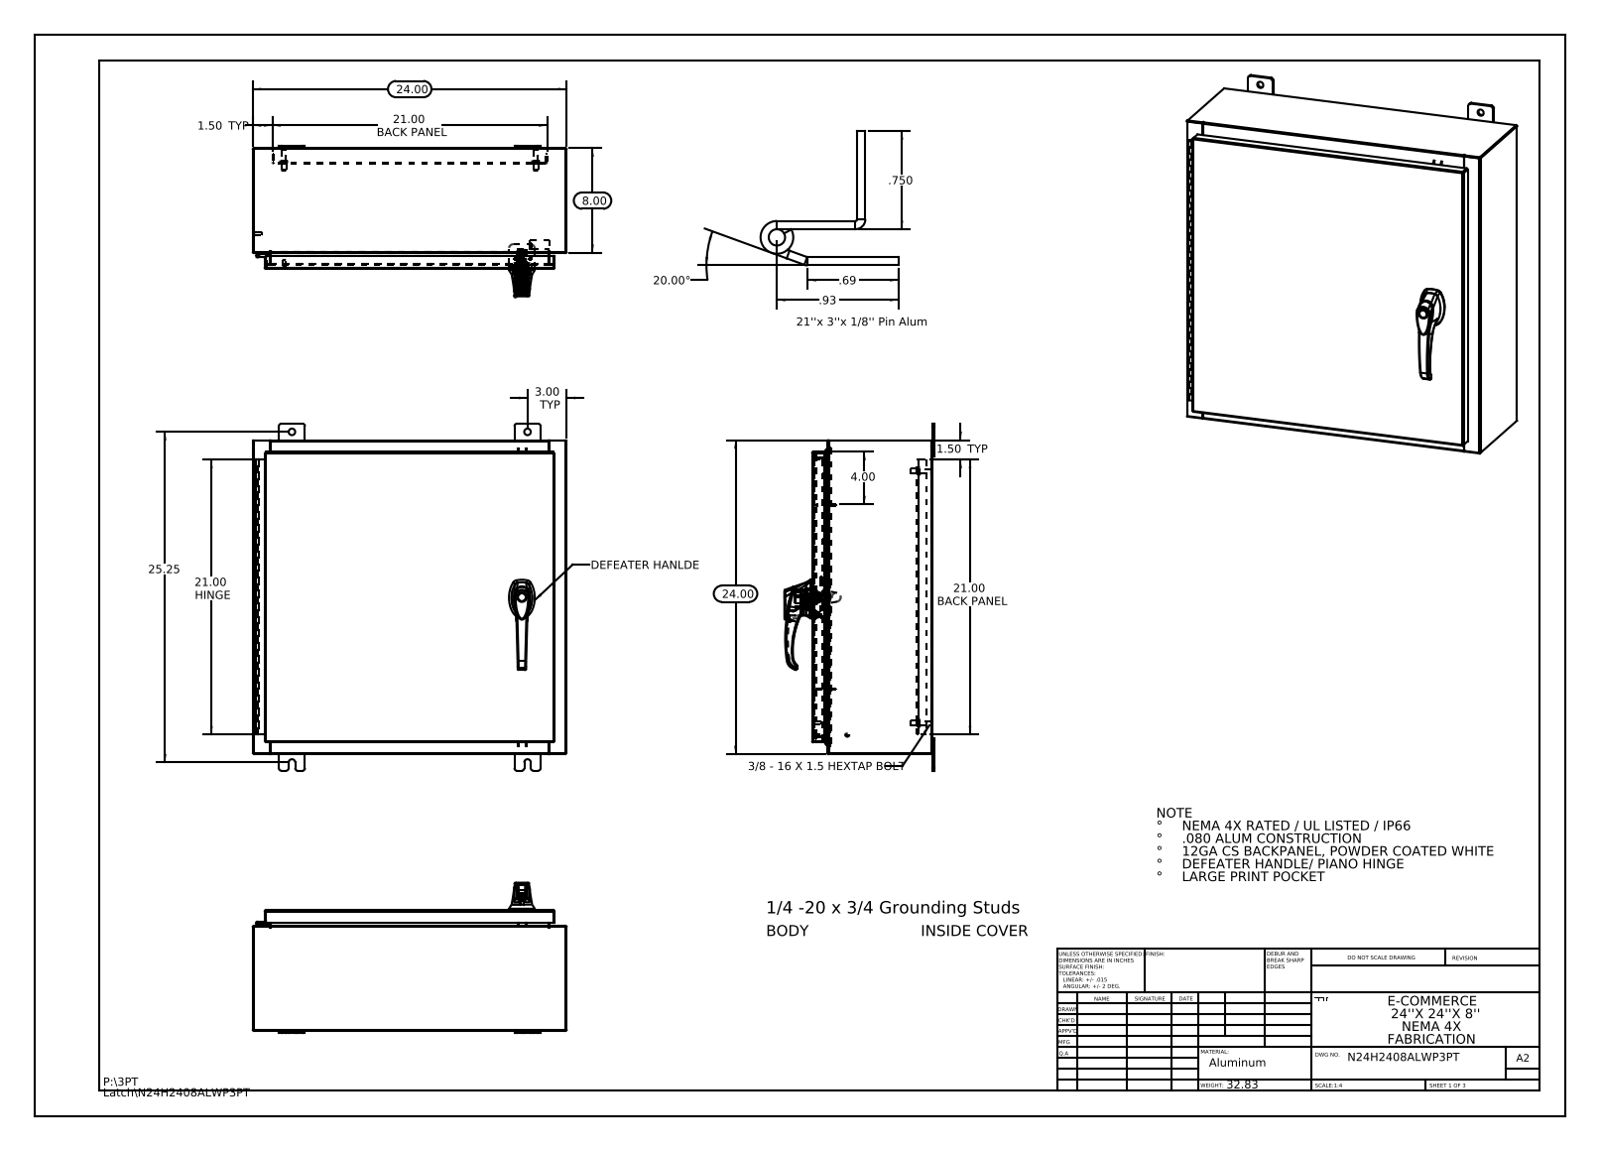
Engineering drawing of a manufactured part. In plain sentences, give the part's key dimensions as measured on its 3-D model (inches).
The part is named "g26103103_26163303; N24H2408ALWP3PT Top; N24H2408ALWP3PT Backpanel; N24H2408ALWP3PT Hinge Enclosure Side2 (+8 more)". Its 3-D file was written by "SolidWorks 2013 (CONFIG_CONTROL_DESIGN)". It is 37 solids with 2498 faces: 883 planar, 917 cylindrical and 698 other. Overall it measures 26.5 by 24 by 11.495 inches. Its volume is 223.4 cubic inches and its surface area 5 522 square inches. Round holes: 8 of diameter 0.5, 4 of diameter 0.25, 3 of diameter 0.138, 3 of diameter 0.161, 2 of diameter 0.079, 2 of diameter 0.203, 2 of diameter 0.313, 2 of diameter 0.437, 1 of diameter 0.125, 1 of diameter 0.125, 1 of diameter 0.197, 1 of diameter 0.276. Round bosses or shafts: 4 of diameter 0.625, 4 of diameter 0.375, 4 of diameter 0.33, 4 of diameter 0.157, 4 of diameter 0.14, 3 of diameter 0.315, 3 of diameter 0.236, 1 of diameter 1.181. Partial cylindrical surfaces (rounded edges, fillets, slot ends): 37 of radius 0.118, 33 of radius 0.006, 24 of radius 0.19, 22 of radius 0.013, 18 of radius 0.088, 15 of radius 0.039, 12 of radius 0.028, 6 of radius 0.008. The main face-to-face distances are 0.075, 9.126, 23.925, 9.051, 9.201, 0.104, 1, 1.075, 8.051, 8.126. The hole center spacings are 7.68, 0.295, 0.625, 0.841, 1.25, 1.313, 1.561, 1.858.
